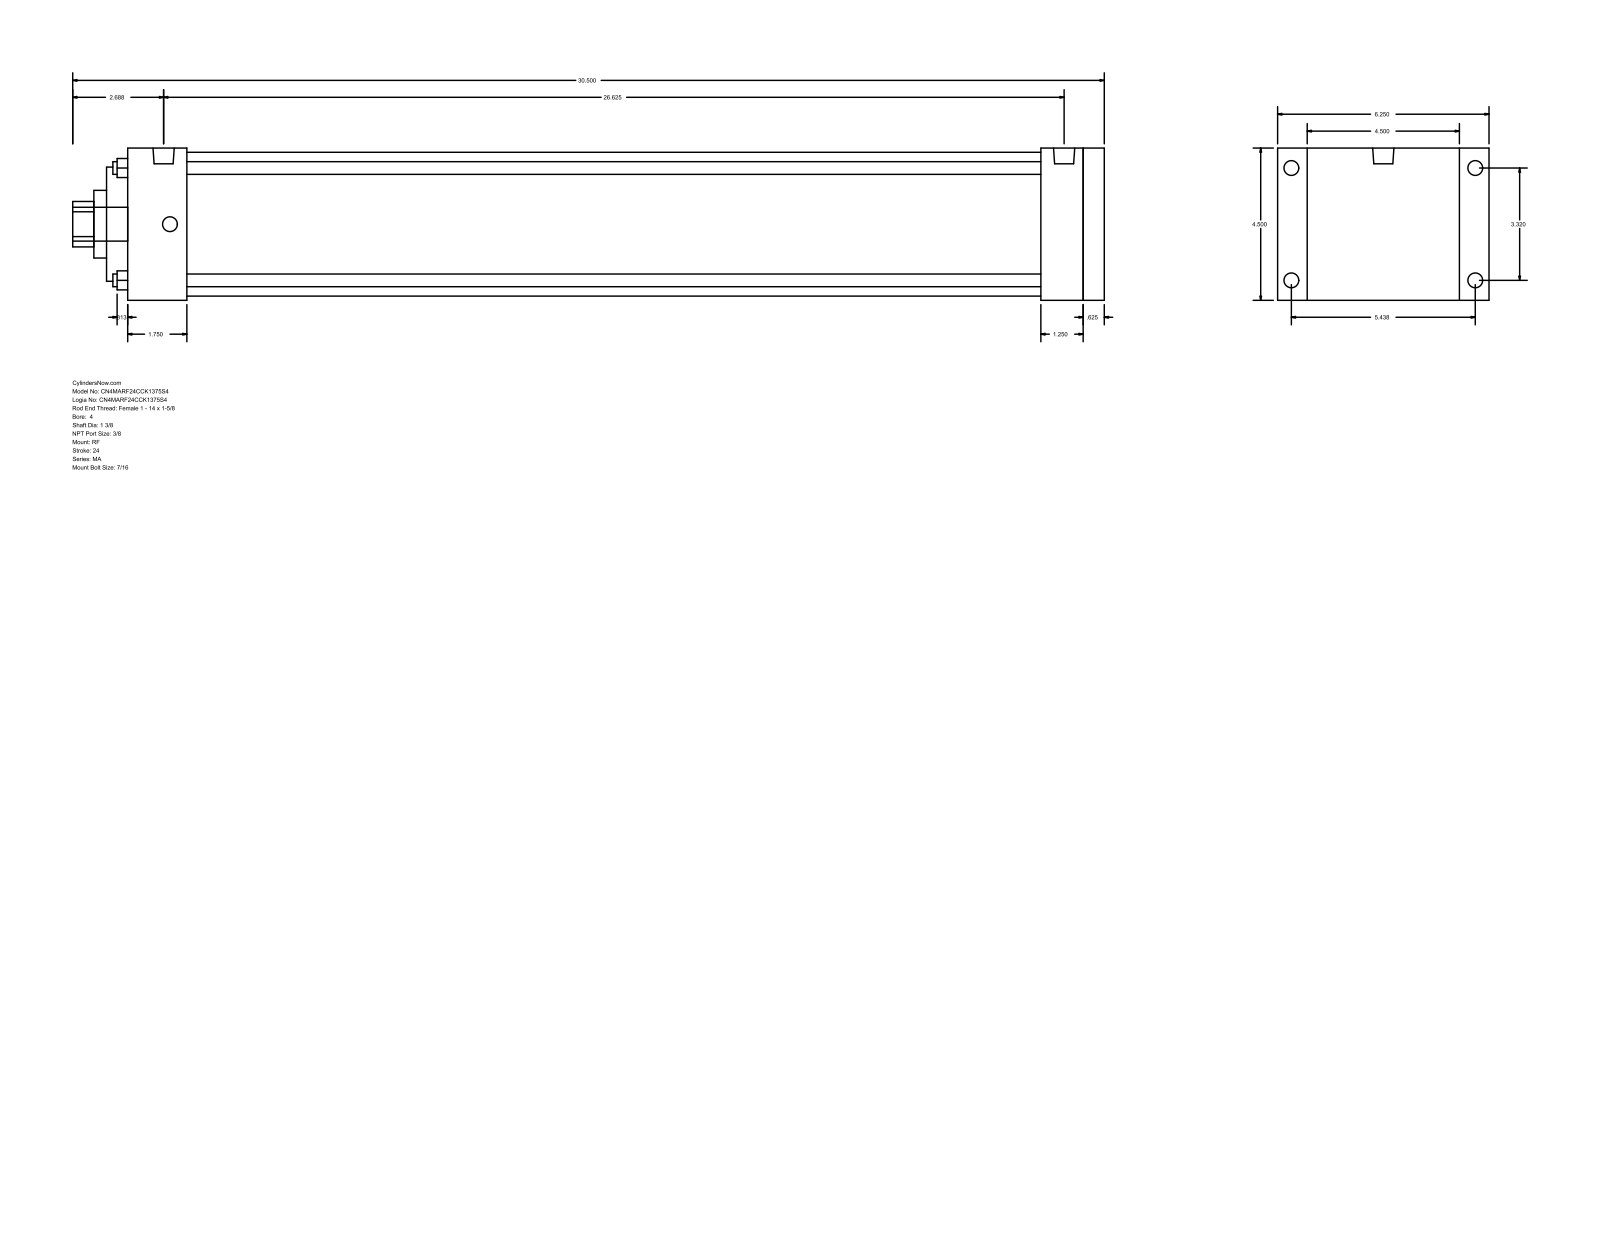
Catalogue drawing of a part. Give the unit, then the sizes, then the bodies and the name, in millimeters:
Units: millimetres
Overall size (bounding box): 774.7 × 158.75 × 114.3
Round holes (diameter × count): ⌀9.53 ×4, ⌀34.92 ×1, ⌀50.8 ×1, ⌀85.72 ×1, ⌀107.95 ×1
Round bosses / shafts (diameter × count): ⌀11.11 ×8, ⌀15.93 ×2, ⌀25.4 ×1
Partial cylindrical surfaces — rounded edges, fillets, slot ends (radius × count): R17.06 ×1
Main face-to-face distances: 114.3, 733.43, 15.87, 717.56, 749.3, 22.23, 136.53, 701.68, 685.81, 31.75
Hole centre spacings: 59.62, 84.32, 119.25
Bodies: 0 solids, 94 faces (65 planar, 29 cylindrical, 0 other)
Part name (STEP PRODUCT): MA_RF__0400_1.375
STEP written by: GSSL Pune (CONFIG_CONTROL_DESIGN)
